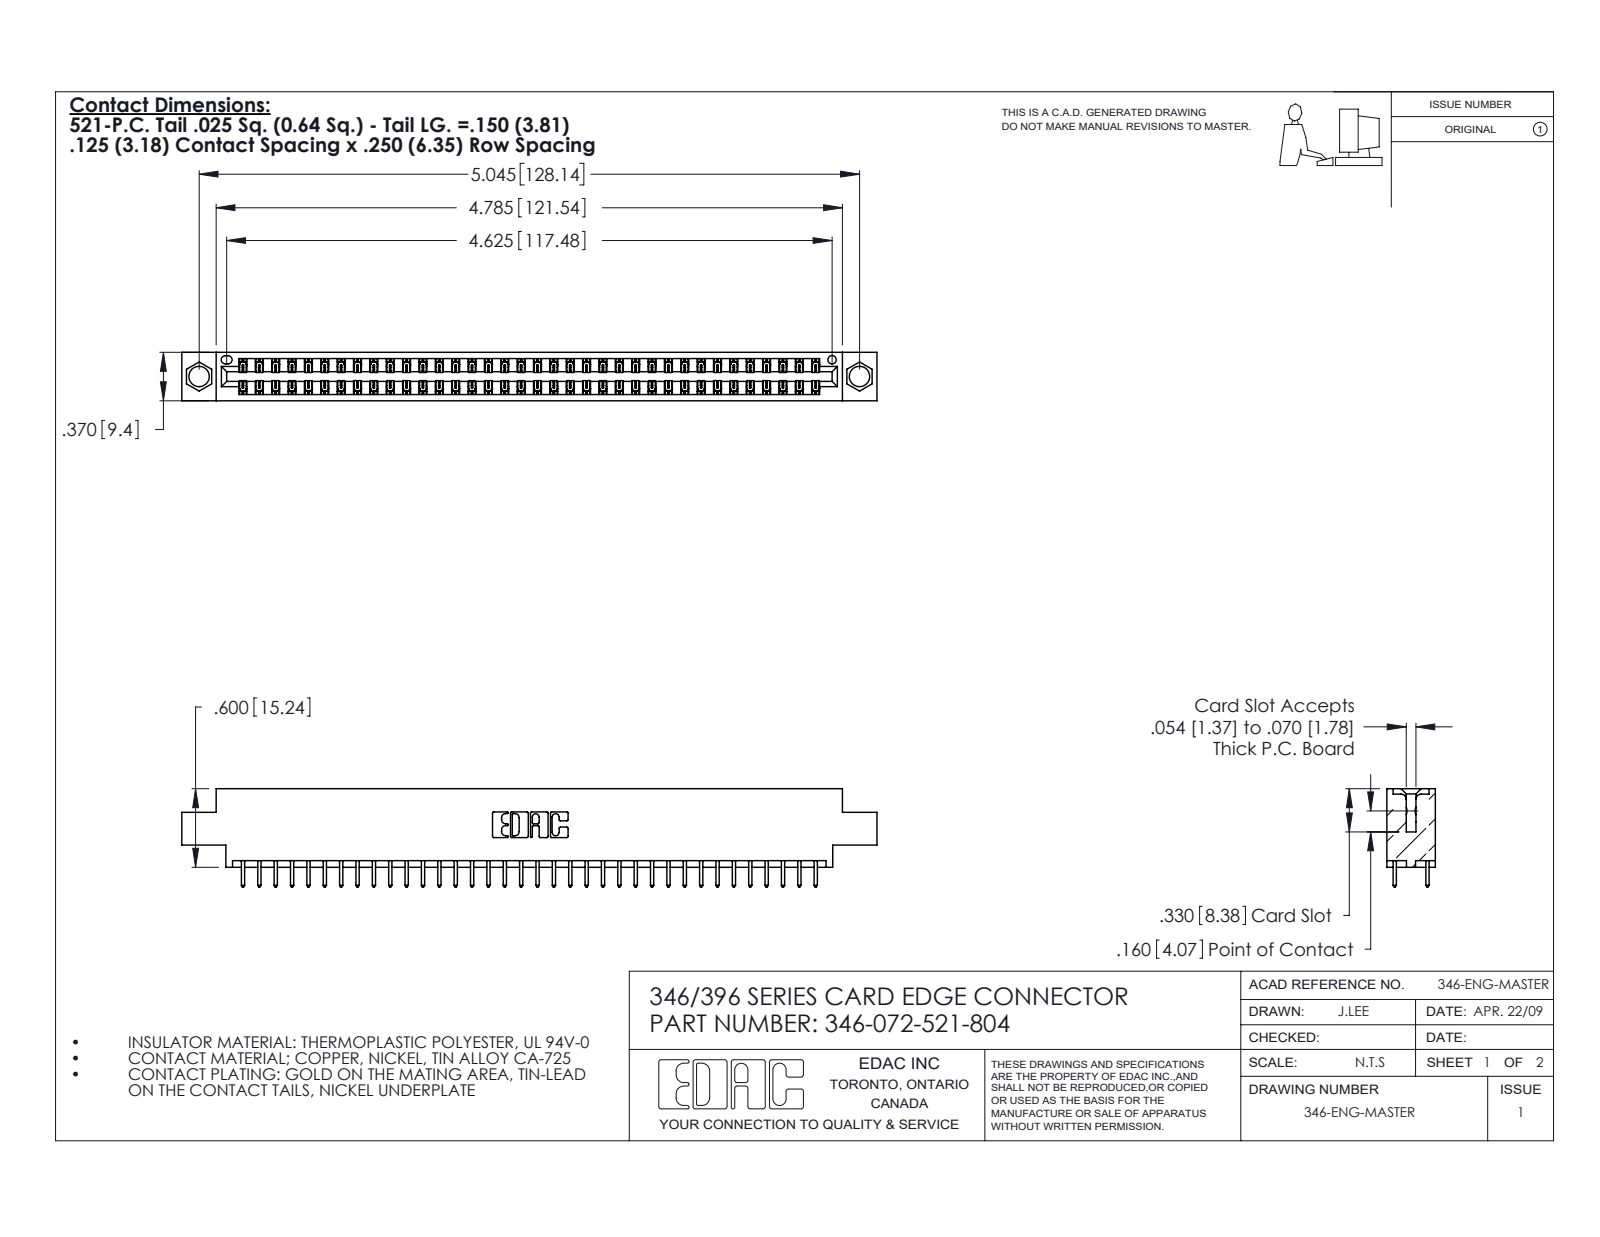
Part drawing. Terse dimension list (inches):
name: 346 Part_0.170 Offset - 0.156 Dia-TH; 346-072-521-804; 345-292-001_345-293-121
written by: SolidWorks 2020 (CONFIG_CONTROL_DESIGN)
unit: in
bodies: 73 solids, 3884 faces (2614 planar, 1270 cylindrical, 0 other)
size: 5.31 × 0.75 × 0.37
volume: 0.782 in³; area: 26.89 in²
holes: 2× ⌀0.156, 1× ⌀0.064
rounds: 108× R0.006, 72× R0.01, 22× R0.01, 6× R0.007, 6× R0.031, 3× R0.026, 2× R0.014, 2× R0.022
face distances: 0.048, 0.322, 0.37, 0.25, 0.072, 0.298, 0.025, 0.275, 0.222, 0.148
hole spacings: 0.246, 4.836, 5.045
